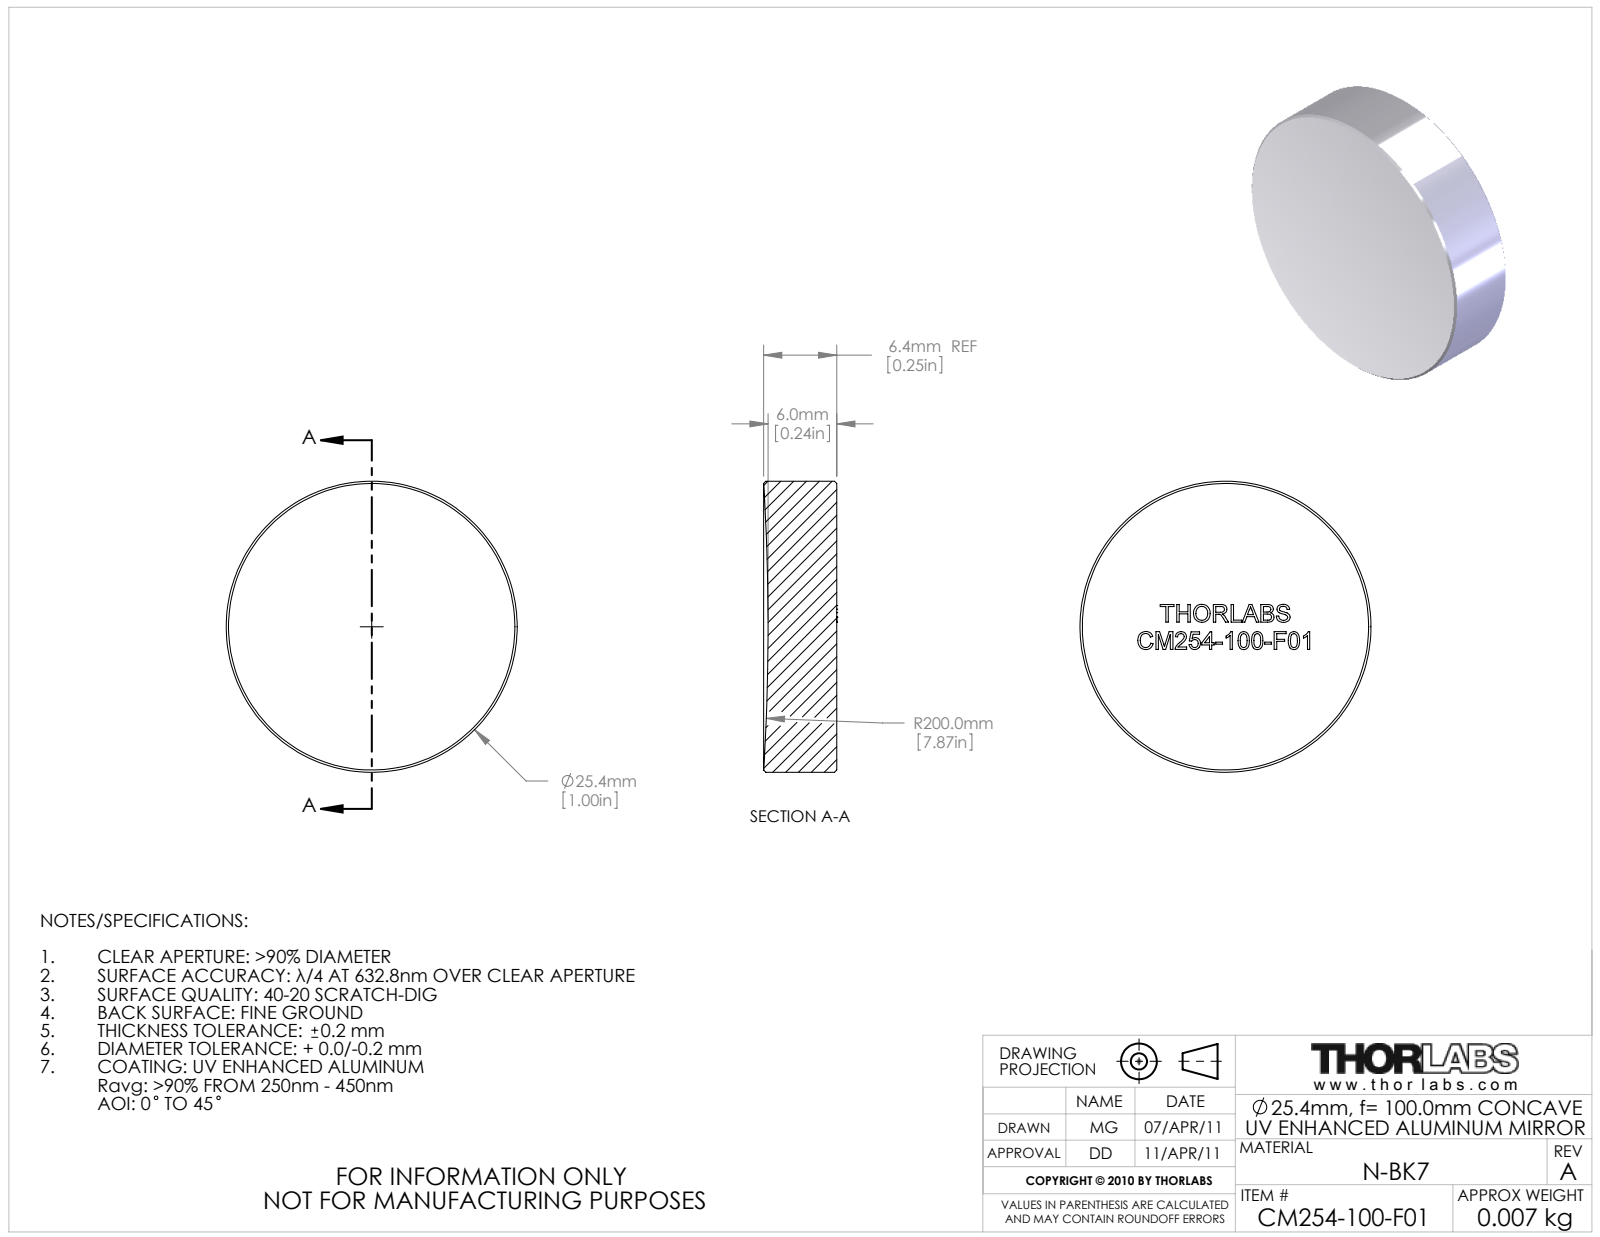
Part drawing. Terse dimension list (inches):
name: 22197-E0W
written by: SolidWorks 2011 (AUTOMOTIVE_DESIGN)
unit: in
bodies: 1 solid, 270 faces (158 planar, 2 cylindrical, 110 other)
size: 1 × 1 × 0.252
volume: 0.192 in³; area: 2.333 in²
bosses: 1× ⌀1
face distances: 0.061, 0.076, 0.093, 0.06, 0.163, 0.069, 0.034, 0.037, 0.046, 0.029
